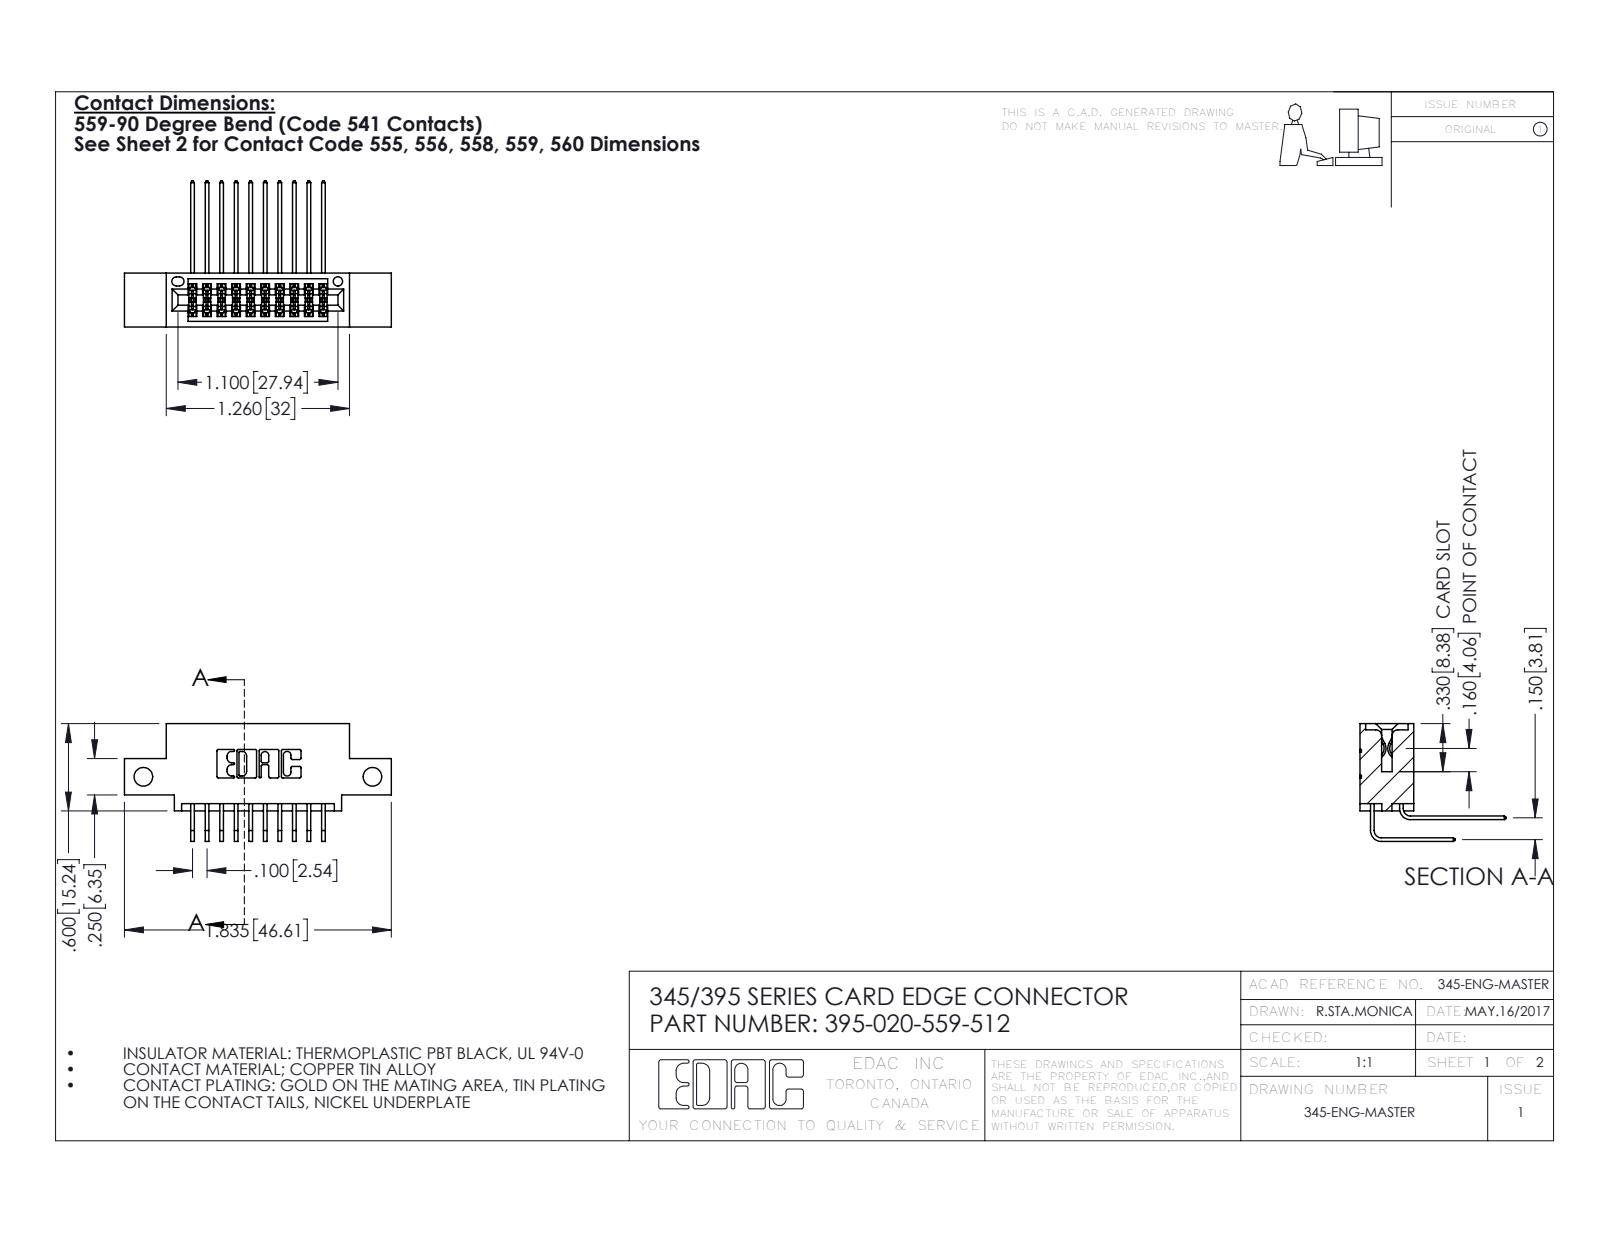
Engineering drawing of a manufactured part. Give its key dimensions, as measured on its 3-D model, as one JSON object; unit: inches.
{"part_name": "345-292-001_559 Tail - 2; 395-020-559-512; 345 Part_0.110 Offset - Side Mount; 345-292-001_558 559 Tail - 1", "step_written_by": "SolidWorks 2016 (CONFIG_CONTROL_DESIGN)", "units": "inches", "bodies": {"solids": 21, "faces": 1170, "planar": 784, "cylindrical": 386, "other": 0}, "overall_size": [1.835, 1.005, 0.809], "volume_in3": 0.255, "surface_area_in2": 9.403, "round_holes": [[0.128, 2], [0.064, 1]], "partial_cylinders_radius": [[0.006, 31], [0.01, 22], [0.007, 6], [0.031, 6], [0.026, 3], [0.014, 2], [0.019, 2], [0.022, 2]], "face_to_face_distances": [0.2, 0.072, 0.298, 0.37, 0.1, 0.098, 0.272, 0.025, 0.6, 0.15], "hole_center_spacings": [1.575]}
